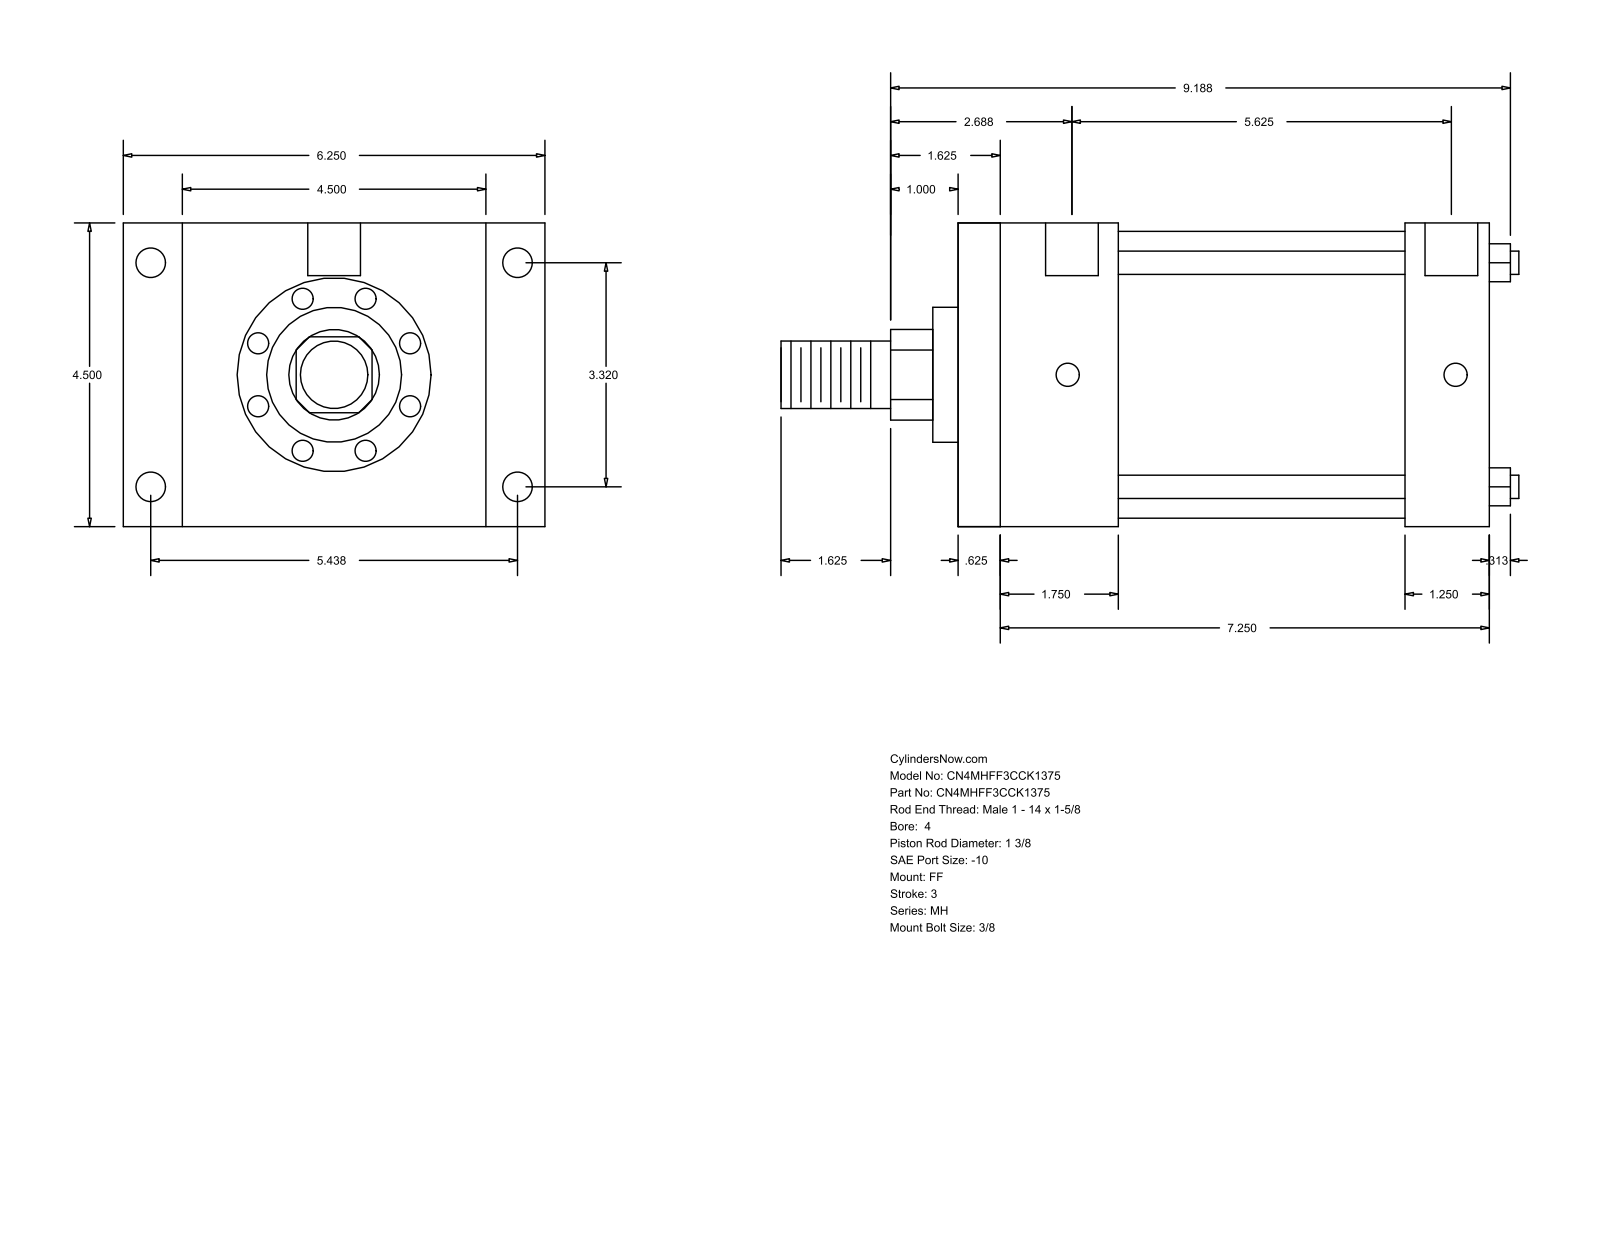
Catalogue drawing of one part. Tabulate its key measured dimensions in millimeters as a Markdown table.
| quantity | value |
| --- | --- |
| part name | MH_FF__0400_1.375 |
| STEP written by | GSSL Pune (CONFIG_CONTROL_DESIGN) |
| units | millimeters |
| bodies | 0 solids, 92 faces (64 planar, 28 cylindrical, 0 other) |
| overall size | 277.81 × 158.75 × 114.3 |
| round holes (diameter × count) | 8.73 × 4, 11.13 × 4, 19.84 × 2 |
| round bosses / shafts (diameter × count) | 8.76 × 4, 107.95 × 1, 50.8 × 1, 34.92 × 1, 25.4 × 1 |
| partial cylindrical surfaces (radius × count) | 17.06 × 1 |
| main face-to-face distances | 114.3, 200.03, 15.87, 184.16, 60.32, 44.45, 139.71, 168.28, 152.41, 107.96 |
| hole center spacings | 84.32, 138.12, 146.05, 161.82, 1.58, 1.59, 142.88, 144.46 |
